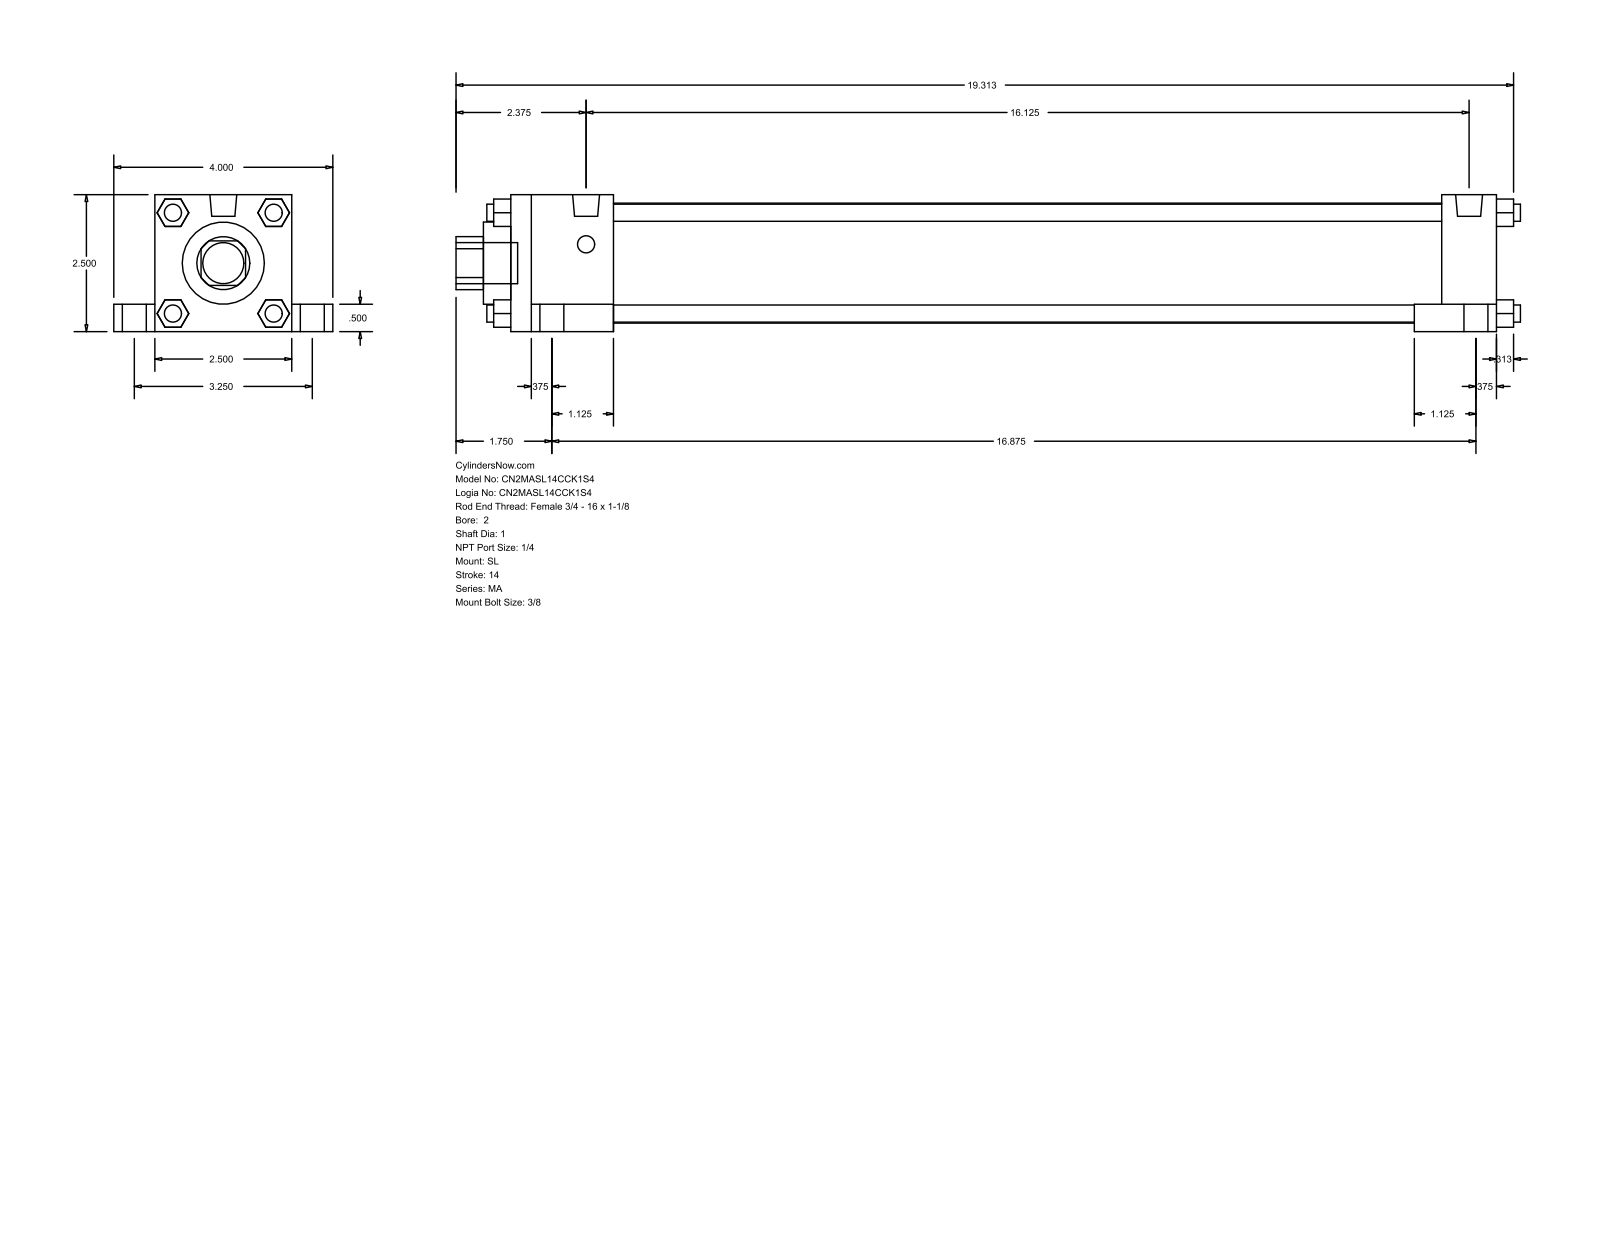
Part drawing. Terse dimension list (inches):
name: MA_SL__0200_1
written by: GSSL Pune (CONFIG_CONTROL_DESIGN)
unit: in
bodies: 0 solids, 148 faces (112 planar, 36 cylindrical, 0 other)
size: 19.437 × 4 × 2.5
holes: 1× ⌀1, 1× ⌀1.5, 1× ⌀2.19
bosses: 8× ⌀0.313, 4× ⌀0.687, 4× ⌀0.437, 2× ⌀0.492, 1× ⌀0.75
rounds: 1× R0.484
face distances: 2.5, 0.5, 18, 0.75, 3.25, 1, 2, 1.875, 16.125, 17
